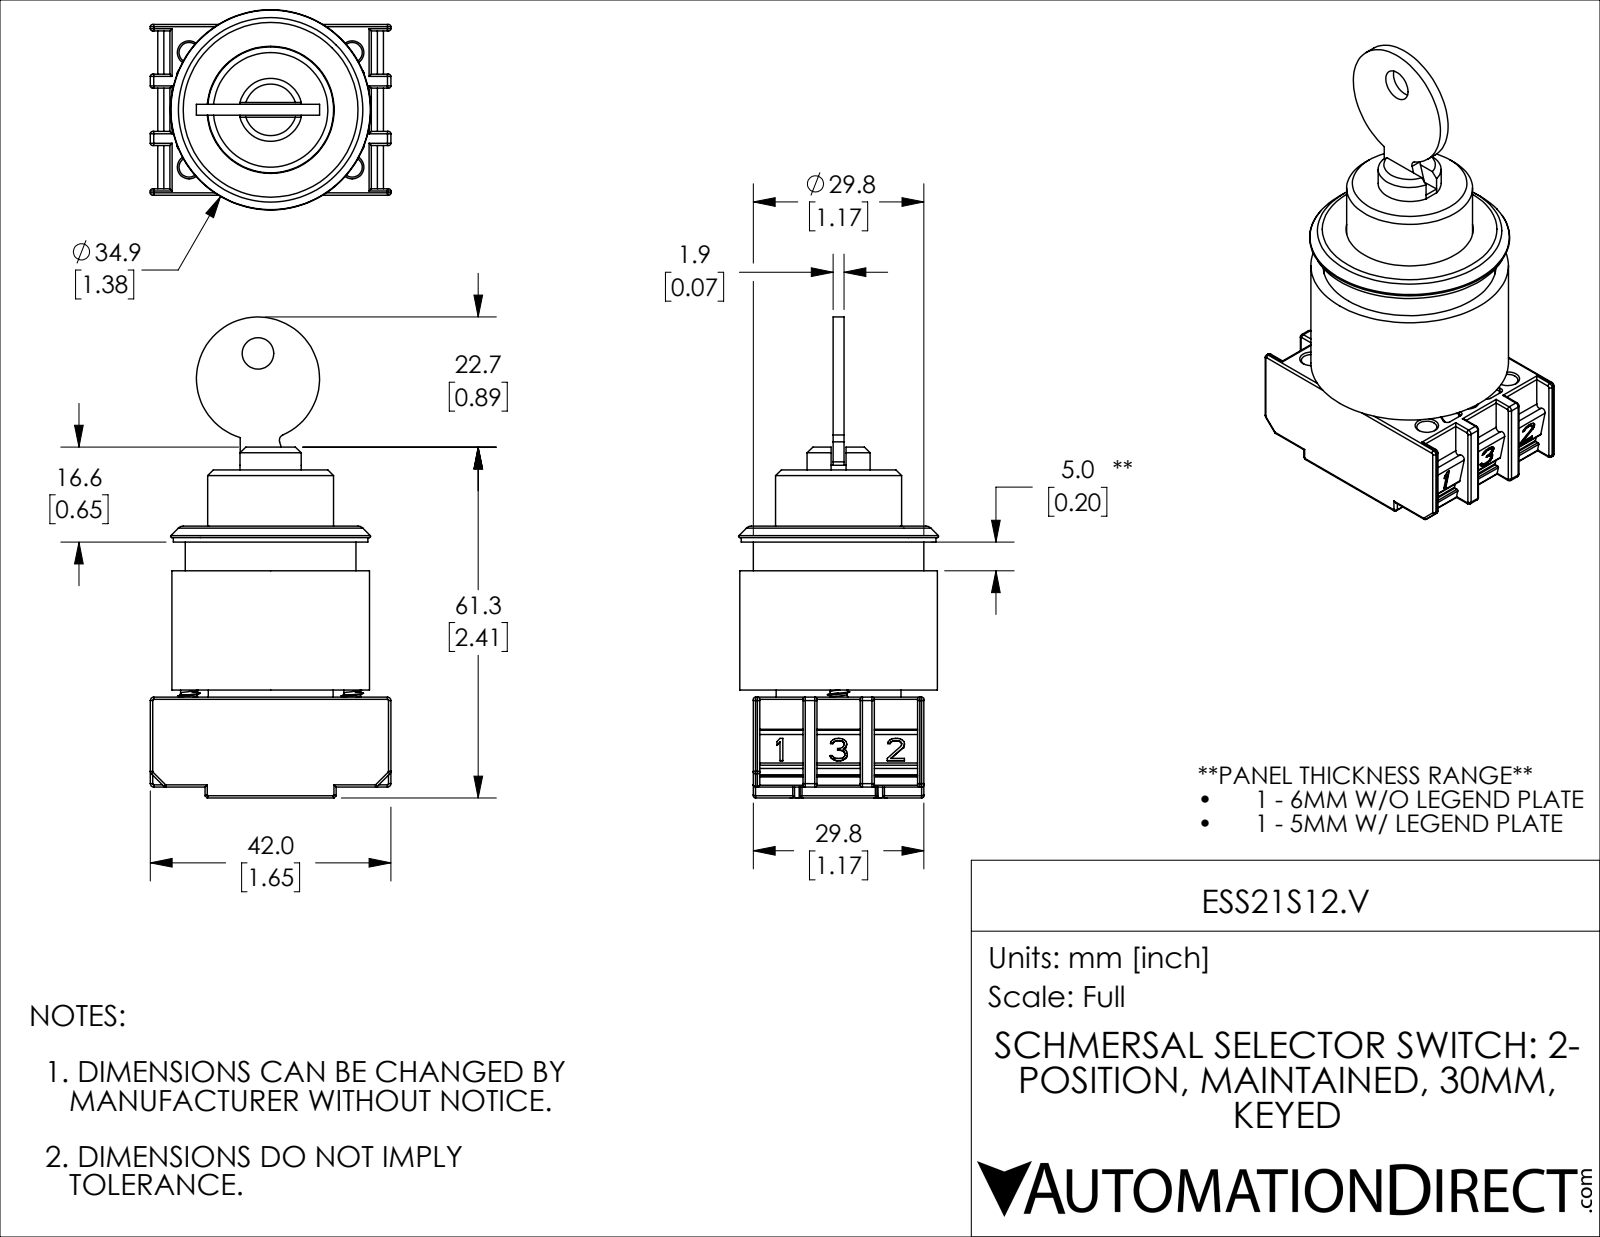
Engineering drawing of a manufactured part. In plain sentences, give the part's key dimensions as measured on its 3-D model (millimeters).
The part is named "ESS21S12.V". Its 3-D file was written by "SolidWorks 2019 (CONFIG_CONTROL_DESIGN)". It is 6 solids with 1547 faces: 569 planar, 536 cylindrical and 442 other. Overall it measures 83.94 by 42 by 34.93 millimeters. Its volume is 39 218 cubic millimeters and its surface area 28 778 square millimeters. Round holes: 10 of diameter 3.5, 6 of diameter 5.15, 2 of diameter 2.5, 2 of diameter 2.8, 1 of diameter 2, 1 of diameter 5.5, 1 of diameter 9.9, 1 of diameter 12.1, 1 of diameter 12.5, 1 of diameter 14, 1 of diameter 19, 1 of diameter 22.2. Round bosses or shafts: 2 of diameter 4.8, 2 of diameter 2.93, 1 of diameter 34.5, 1 of diameter 34, 1 of diameter 29.8, 1 of diameter 25.5, 1 of diameter 22, 1 of diameter 21.8. Partial cylindrical surfaces (rounded edges, fillets, slot ends): 110 of radius 0.4, 48 of radius 0.3, 26 of radius 0.2, 9 of radius 0.5, 8 of radius 0.6, 6 of radius 0.8, 2 of radius 0.1, 2 of radius 0.6. The main face-to-face distances are 13.95, 15.85, 10, 29.8, 1.9, 17.6, 16.1, 17.35, 18.85, 5. The hole center spacings are 8.69, 8.99, 10, 10.13, 12.72, 17.41, 18.16, 20.93.
